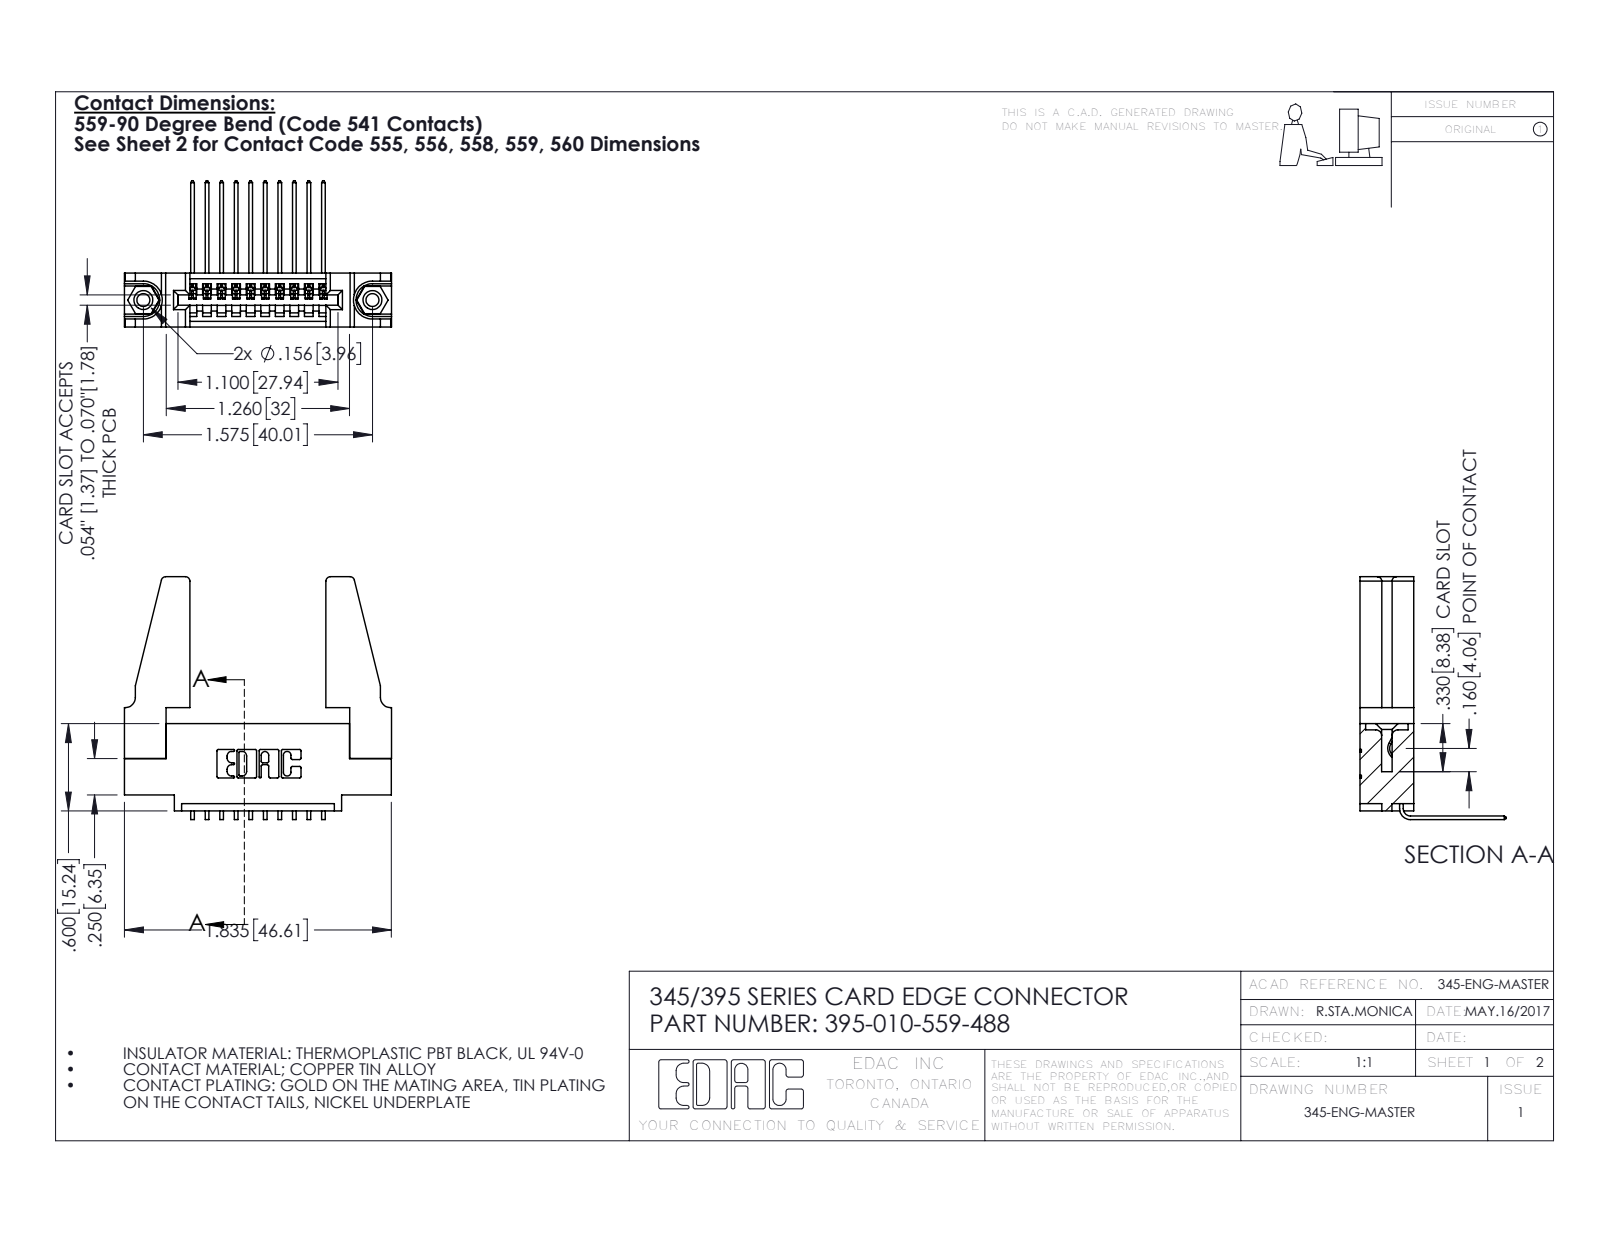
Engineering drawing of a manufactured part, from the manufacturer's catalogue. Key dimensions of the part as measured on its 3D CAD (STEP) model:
Part name (STEP PRODUCT): 395-010-559-488; 345-292-001_558 559 Tail - 1; 345 Part_0.110 Offset - 0.156 Dia-TH; 345-220-078_345-220-088 (+1 more)
STEP written by: SolidWorks 2016 (CONFIG_CONTROL_DESIGN)
Units: inches
Bodies: 15 solids, 854 faces (576 planar, 262 cylindrical, 16 other)
Overall size (bounding box): 1.836 × 1.669 × 1.005
Volume: 0.45 in³ · Surface area: 13.11 in²
Round holes (diameter × count): ⌀0.089 ×2, ⌀0.125 ×2, ⌀0.156 ×2, ⌀0.064 ×1
Round bosses / shafts (diameter × count): ⌀0.155 ×2
Partial cylindrical surfaces — rounded edges, fillets, slot ends (radius × count): R0.01 ×22, R0.006 ×20, R0.03 ×8, R0.007 ×6, R0.031 ×6, R0.026 ×3, R0.031 ×2, R0.04 ×2
Main face-to-face distances: 0.37, 0.072, 0.298, 0.2, 0.098, 0.272, 0.025, 0.148, 0.15, 0.225
Hole centre spacings: 0.27, 1.344, 1.575
